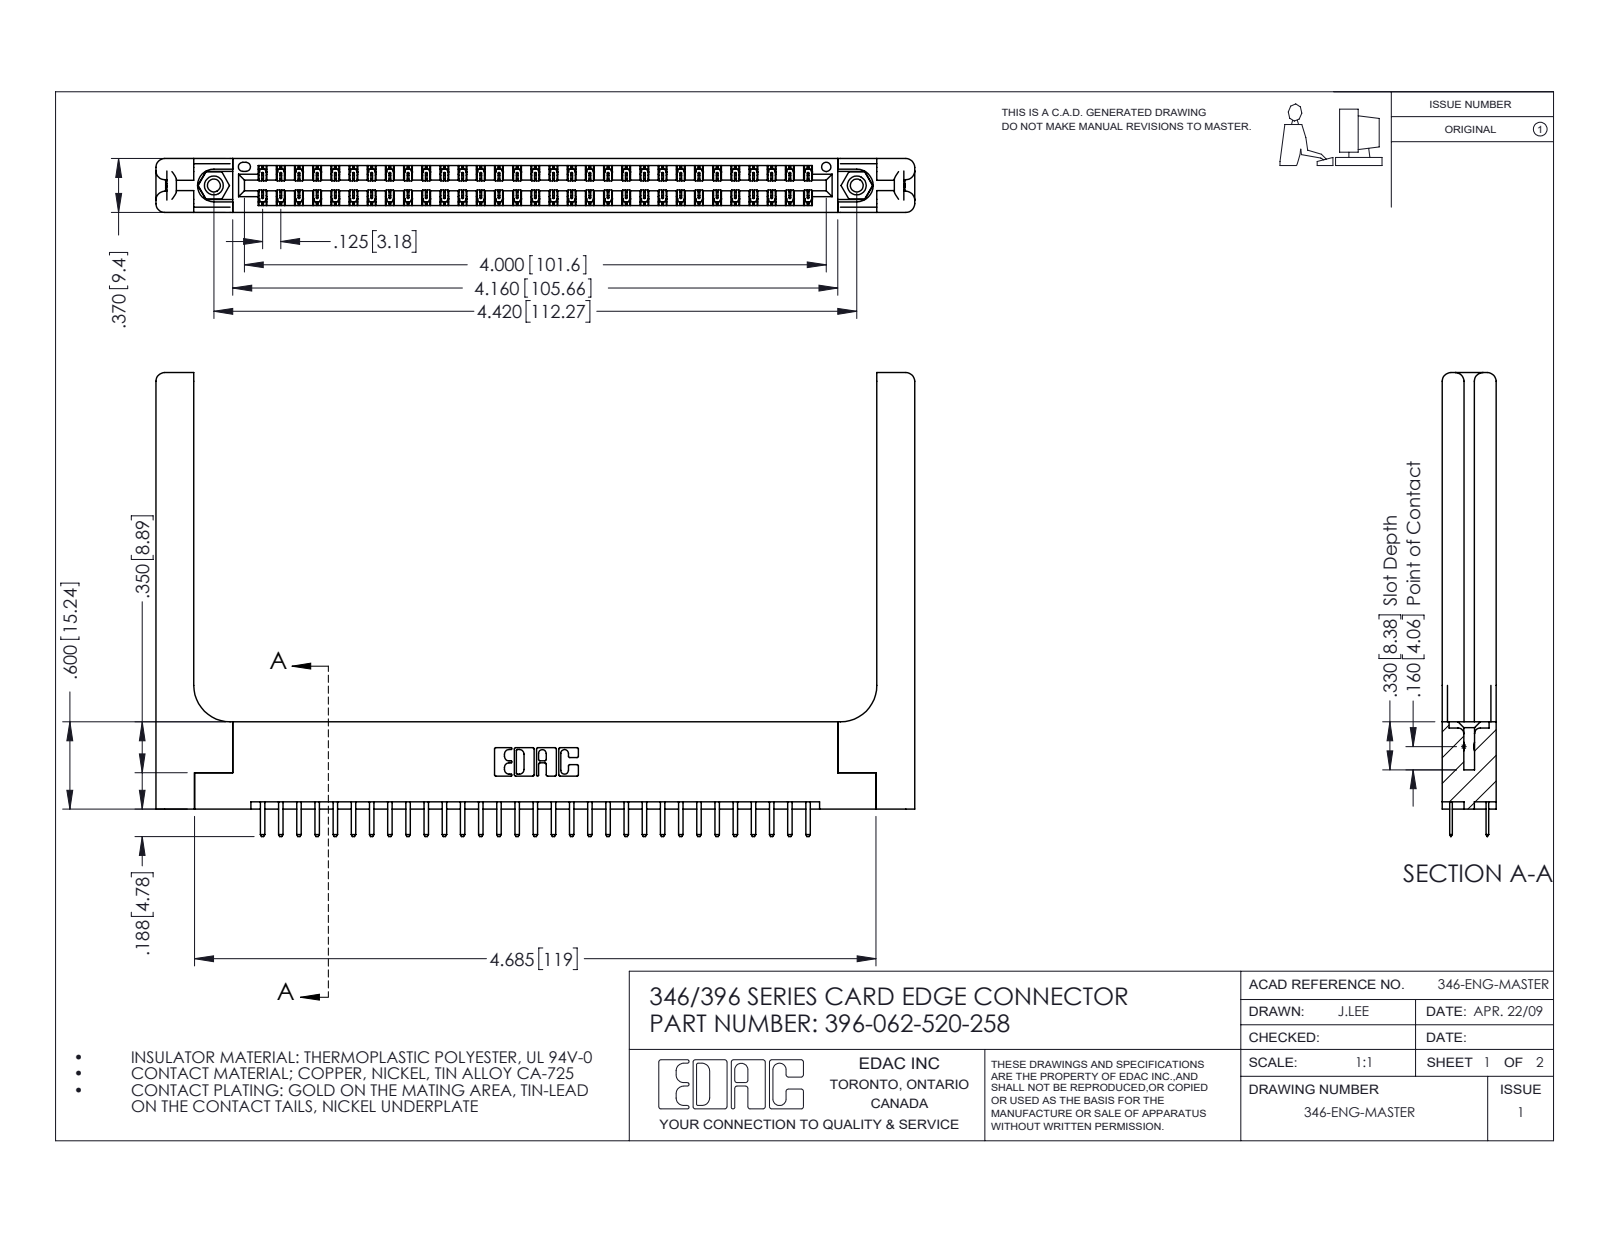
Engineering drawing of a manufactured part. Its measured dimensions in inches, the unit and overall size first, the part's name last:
Units: inches
Overall size (bounding box): 5.216 × 3.188 × 0.37
Round holes (diameter × count): ⌀0.089 ×2, ⌀0.125 ×2, ⌀0.156 ×2, ⌀0.064 ×1
Round bosses / shafts (diameter × count): ⌀0.155 ×2
Partial cylindrical surfaces — rounded edges, fillets, slot ends (radius × count): R0.006 ×93, R0.01 ×66, R0.01 ×22, R0.06 ×16, R0.007 ×6, R0.031 ×6, R0.026 ×3, R0.014 ×2
Main face-to-face distances: 0.37, 0.048, 0.322, 0.072, 0.25, 0.148, 0.15, 0.298, 0.025, 0.275
Hole centre spacings: 0.246, 4.212, 4.42
Volume: 1.239 in³ · Surface area: 34.63 in²
Bodies: 67 solids, 3850 faces (2518 planar, 1272 cylindrical, 60 other)
Part name (STEP PRODUCT): 345-292-001_345-293-120; 345-250-001_345-250-001-102; 346 Part_Flush Mounting Lugs - 0.156 Dia-TH; 396-062-520-258 (+1 more)
STEP written by: SolidWorks 2016 (CONFIG_CONTROL_DESIGN)
